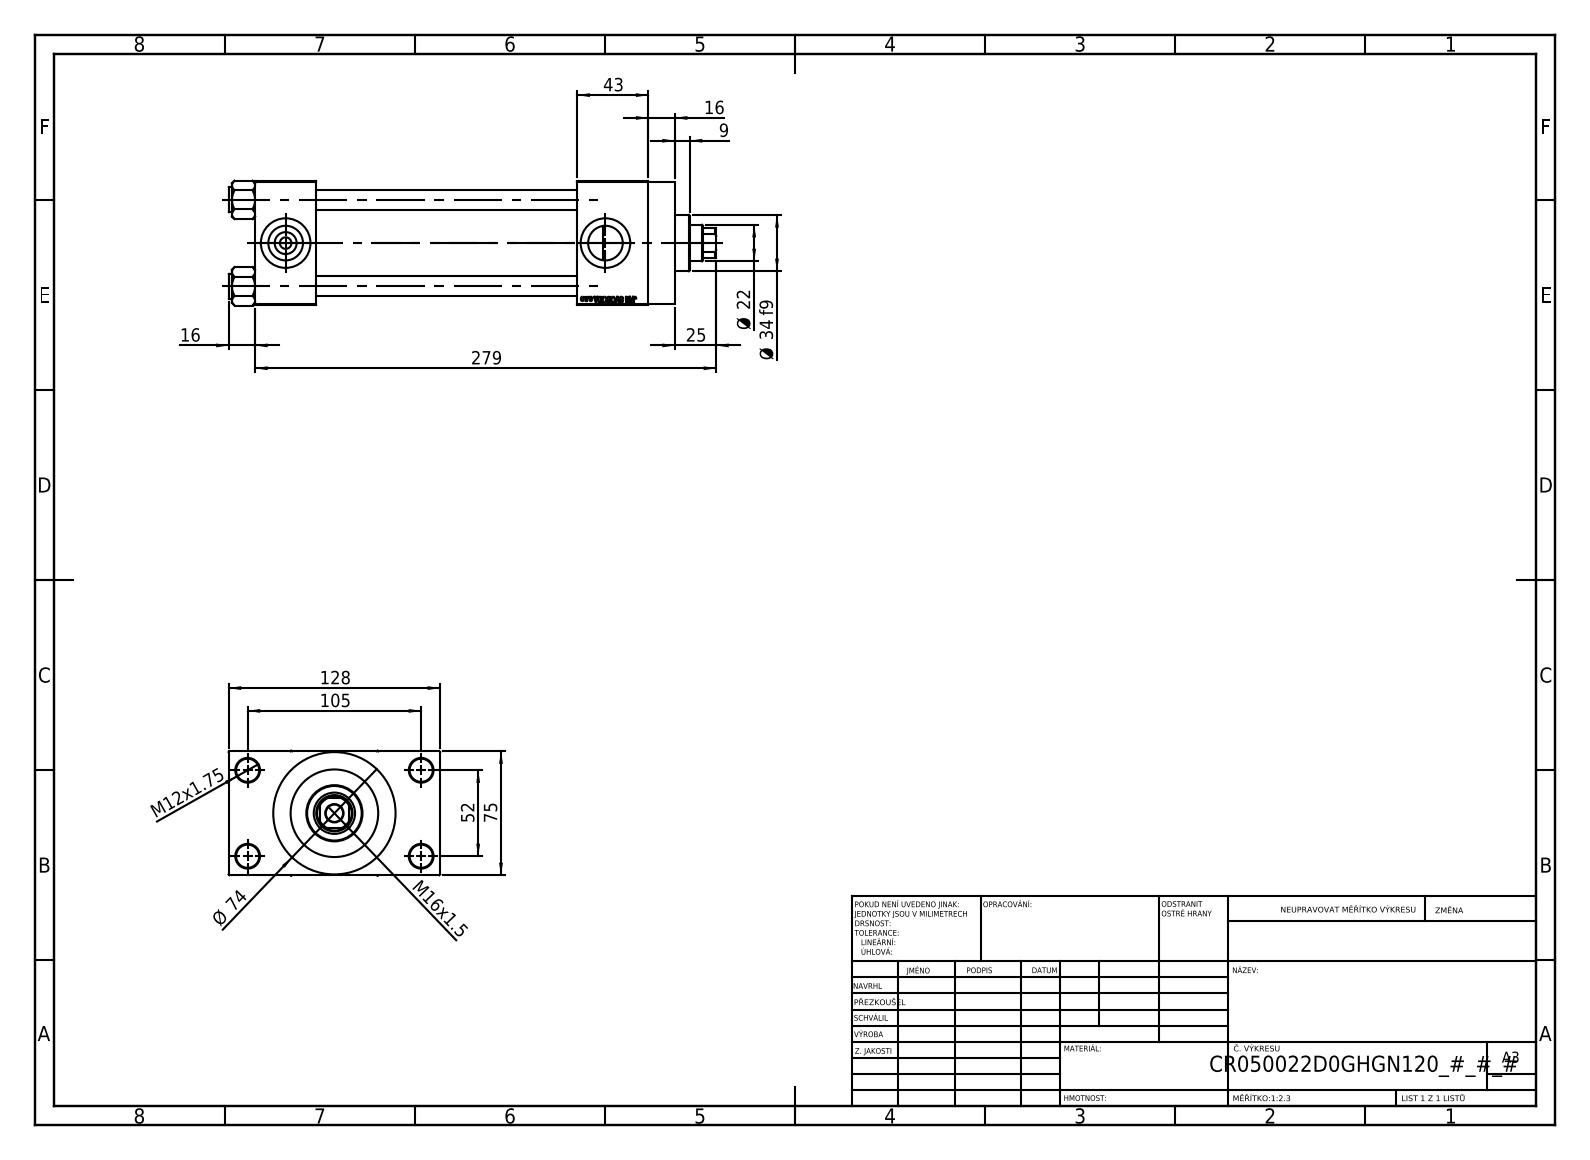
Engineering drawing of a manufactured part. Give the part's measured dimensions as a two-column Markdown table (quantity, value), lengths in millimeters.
| quantity | value |
| --- | --- |
| part name | V215CR_D_Body; V215CR_VCP_D; V215_VC_A; NUT_M5_D (+1 more) |
| STEP written by | SolidWorks 2019 (CONFIG_CONTROL_DESIGN) |
| units | millimeters |
| bodies | 11 solids, 1103 faces (497 planar, 88 cylindrical, 518 other) |
| overall size | 295 × 128 × 75.54 |
| volume | 930 722 mm³ |
| surface area | 221 979 mm² |
| round holes (diameter × count) | 12 × 4, 14 × 4, 7 × 2, 20.96 × 2, 30 × 2, 10.5 × 1, 22 × 1, 25 × 1, 41 × 1, 50 × 1, 53 × 1 |
| round bosses / shafts (diameter × count) | 15 × 4, 74 × 1, 56 × 1, 34 × 1 |
| partial cylindrical surfaces (radius × count) | 10.5 × 1 |
| main face-to-face distances | 75, 158, 37, 195, 26.5, 238, 201, 43, 101.5, 16 |
| hole center spacings | 26.35, 36.98, 52.3, 58.43, 58.59, 78.65, 94.37, 52 |
